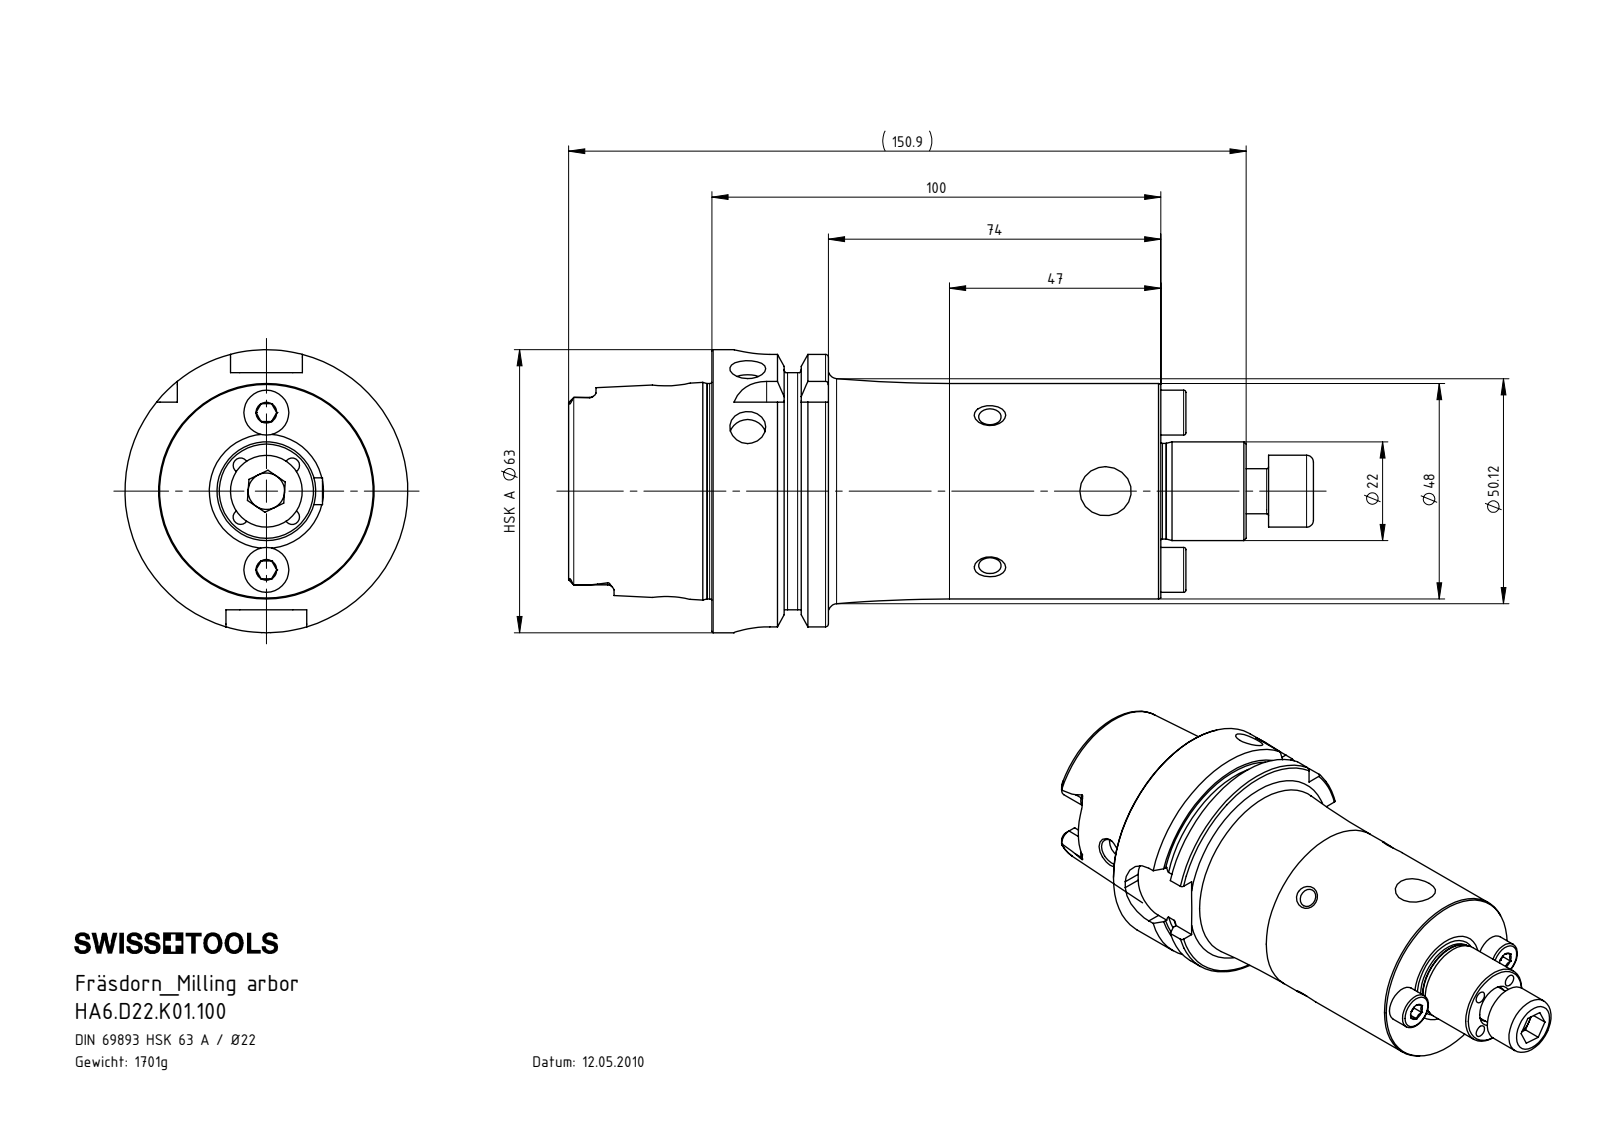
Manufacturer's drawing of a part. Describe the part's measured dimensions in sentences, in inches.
The part is named "D22-ER2.001.017_B; HA6-D22.K01.100_C_Fertigbearbeitung; D22-ER1.002.025_A_Default; HA6.D22.K01.100". Its 3-D file was written by "SolidWorks 2011 (AUTOMOTIVE_DESIGN)". It is 4 solids with 383 faces: 91 planar, 109 cylindrical and 183 other. Overall it measures 6.531 by 2.48 by 2.48 inches. Its volume is 13.41 cubic inches and its surface area 65.38 square inches. Round holes: 4 of diameter 0.197, 4 of diameter 0.315, 3 of diameter 0.13, 2 of diameter 0.165, 1 of diameter 0.295, 1 of diameter 0.331, 1 of diameter 0.394, 1 of diameter 0.413, 1 of diameter 0.669, 1 of diameter 0.748, 1 of diameter 1.339, 1 of diameter 1.575. Round bosses or shafts: 3 of diameter 0.394, 2 of diameter 0.197, 2 of diameter 0.15, 1 of diameter 2.48, 1 of diameter 2.163, 1 of diameter 1.89, 1 of diameter 1.887, 1 of diameter 0.866. Partial cylindrical surfaces (rounded edges, fillets, slot ends): 6 of radius 0.055, 4 of radius 0.113, 4 of radius 0.315, 2 of radius 0.118. The main face-to-face distances are 3.937, 1.022, 2.915, 0.63, 3.545, 0.392, 1.256, 1.648, 2.278, 5.193. The hole center spacings are 0.32, 0.515, 0.689, 0.943, 1.144, 0.64, 1.378.
